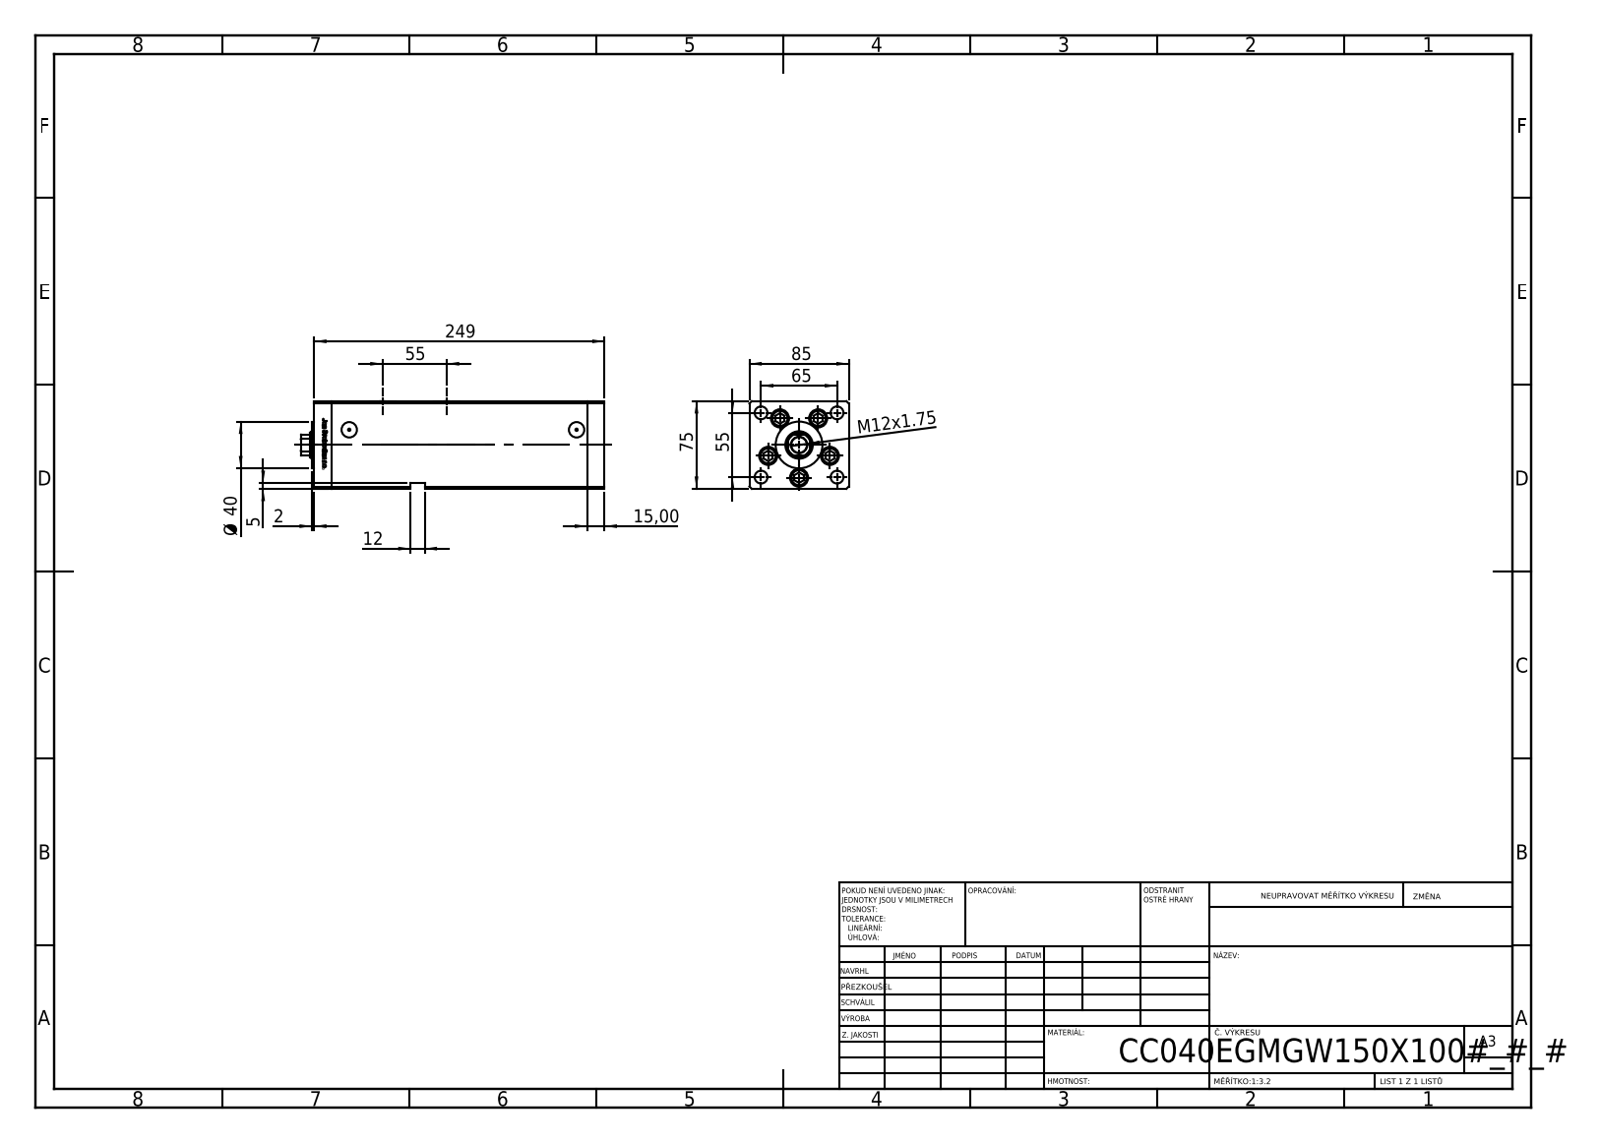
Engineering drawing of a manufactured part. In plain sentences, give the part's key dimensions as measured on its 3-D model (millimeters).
The part is named "V220C_E MIDDLE; V220C_FRONT_E; ALLEN BOLT; V220C BACK_E (+1 more)". Its 3-D file was written by "SolidWorks 2019 (CONFIG_CONTROL_DESIGN)". It is 14 solids with 1214 faces: 475 planar, 165 cylindrical and 574 other. Overall it measures 260 by 85 by 75 millimeters. Its volume is 1 341 000 cubic millimeters and its surface area 209 529 square millimeters. Round holes: 9 of diameter 11, 5 of diameter 15.5, 4 of diameter 10.5, 4 of diameter 16.5, 2 of diameter 2, 2 of diameter 13.16, 1 of diameter 13.5, 1 of diameter 22, 1 of diameter 23.5. Round bosses or shafts: 5 of diameter 14.5, 5 of diameter 8, 1 of diameter 40. Partial cylindrical surfaces (rounded edges, fillets, slot ends): 2 of radius 0.93, 1 of radius 10.5. The main face-to-face distances are 85, 75, 15, 218.5, 233.5, 248.5, 10.5, 64.5, 34.25, 68.5. The hole center spacings are 28, 42.57, 55, 65, 85.15, 16.86, 19.17, 32.33.
